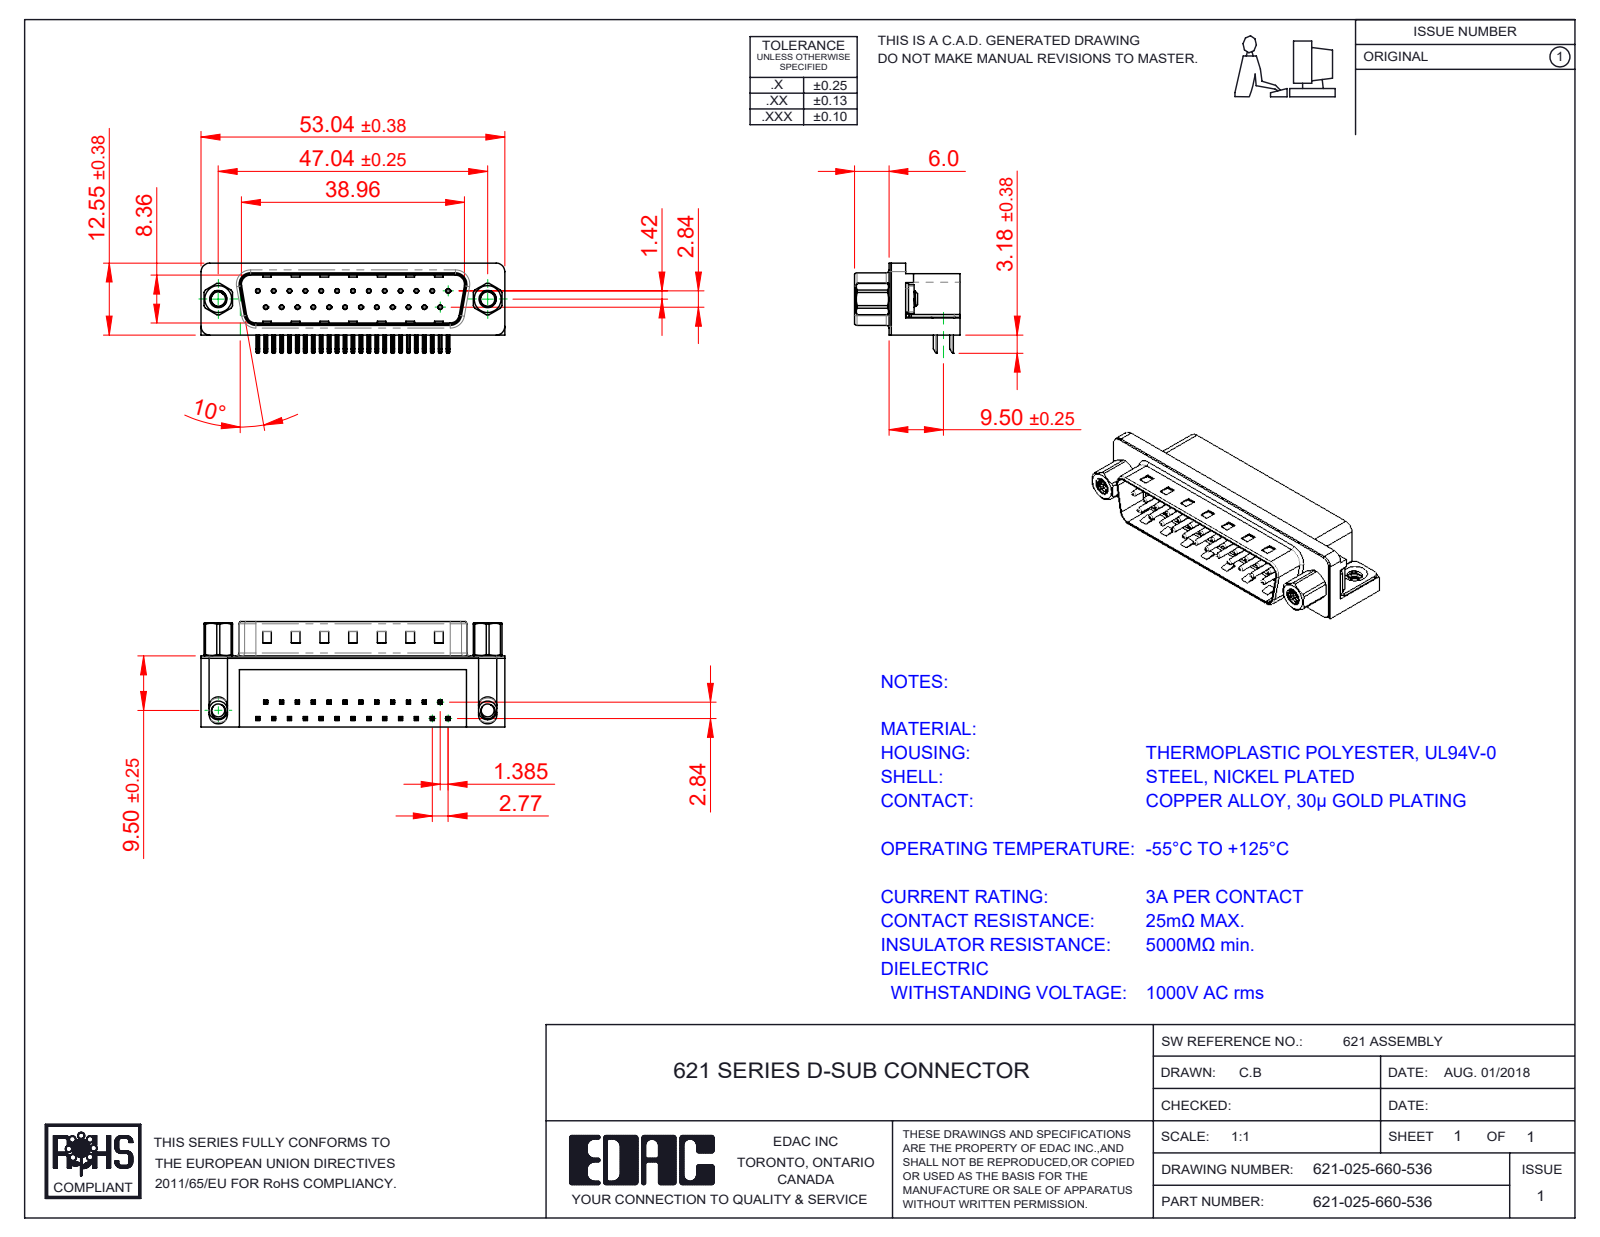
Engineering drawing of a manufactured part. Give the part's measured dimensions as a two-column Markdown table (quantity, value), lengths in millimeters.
| quantity | value |
| --- | --- |
| part name | 621 M3 Threaded Rivet; 621 Contact Bottom; 621 Contact Top; 621 M3 Hex Standoff 5 (+4 more) |
| STEP written by | SolidWorks 2016 (CONFIG_CONTROL_DESIGN) |
| units | millimeters |
| bodies | 33 solids, 2451 faces (1459 planar, 763 cylindrical, 229 other) |
| overall size | 53.04 × 18.4 × 16.25 |
| volume | 6 586 mm³ |
| surface area | 8 221 mm² |
| round holes (diameter × count) | 0.35 × 25, 0.8 × 25, 2.5 × 2, 4 × 2, 4.8 × 2, 5 × 2 |
| round bosses / shafts (diameter × count) | 0.75 × 25, 4.9 × 2, 4.75 × 2, 3.9 × 2, 3 × 2 |
| partial cylindrical surfaces (radius × count) | 0.25 × 108, 0.12 × 50, 1 × 16, 0.5 × 14, 1.6 × 8, 1.5 × 7, 0.32 × 4, 0.9 × 4 |
| main face-to-face distances | 0.4, 12, 10.35, 2.1, 8.76, 10.46, 10.86, 1.7, 12.4, 9 |
| hole center spacings | 3.16, 2.77, 5.54, 8.31, 11.08, 13.85, 16.62, 5.03 |
